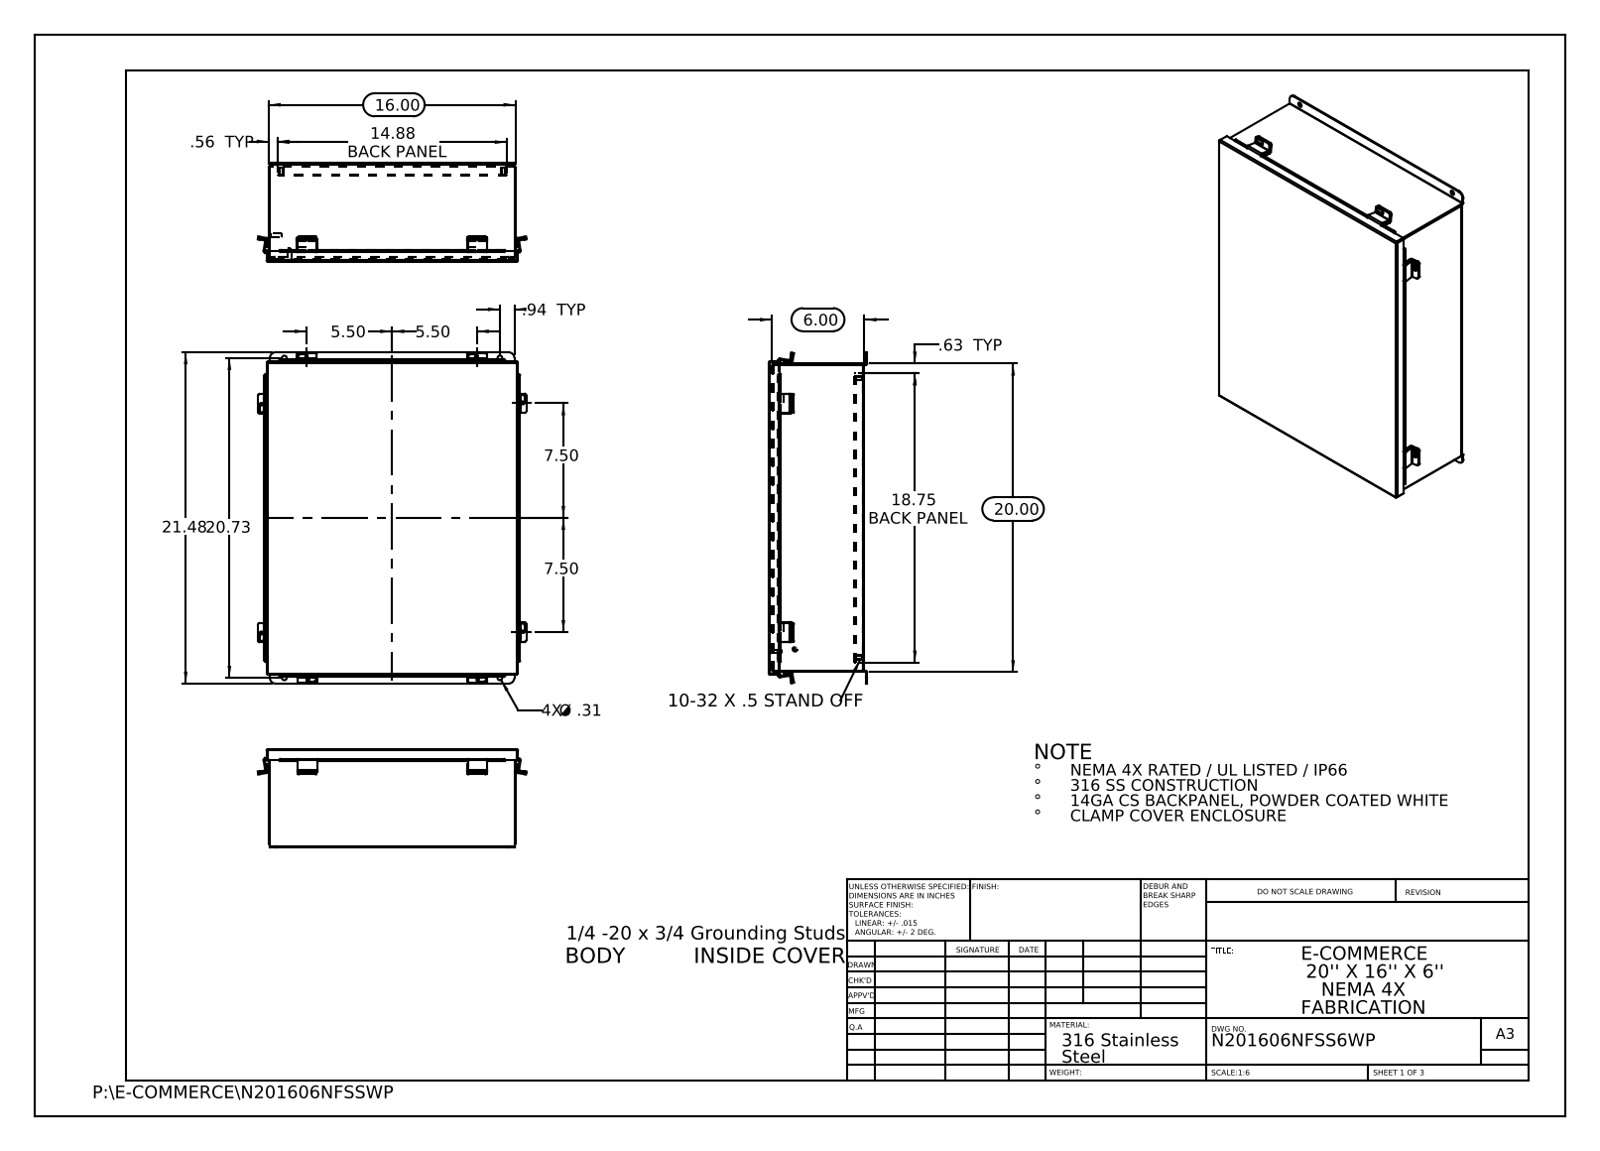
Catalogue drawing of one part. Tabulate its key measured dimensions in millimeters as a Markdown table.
| quantity | value |
| --- | --- |
| part name | N201606NFSSWP JIC Enclosure Template; N201606NFSSWP JIC_Cover_Template; N201606NFSSWP; N201606NFSSWP JIC Cover Clamp (+6 more) |
| STEP written by | SolidWorks 2013 (CONFIG_CONTROL_DESIGN) |
| units | millimeters |
| bodies | 27 solids, 640 faces (420 planar, 200 cylindrical, 20 other) |
| overall size | 545.5 × 442.1 × 162.3 |
| volume | 1 817 000 mm³ |
| surface area | 1 932 000 mm² |
| round holes (diameter × count) | 6.4 × 12, 4.7 × 4, 7.9 × 4 |
| round bosses / shafts (diameter × count) | 8 × 4, 8 × 2, 6 × 2 |
| partial cylindrical surfaces (radius × count) | 3.2 × 28, 0.2 × 16, 3.4 × 16, 0.3 × 12, 2.2 × 12, 2.1 × 8, 2.5 × 8, 2.1 × 4 |
| main face-to-face distances | 1.9, 155.7, 153.7, 157.6, 1.9, 143, 14.6, 12.7, 141, 16.5 |
| hole center spacings | 33.4, 361.6, 493.4, 610.8, 279.4, 355, 365.1, 377.2 |
